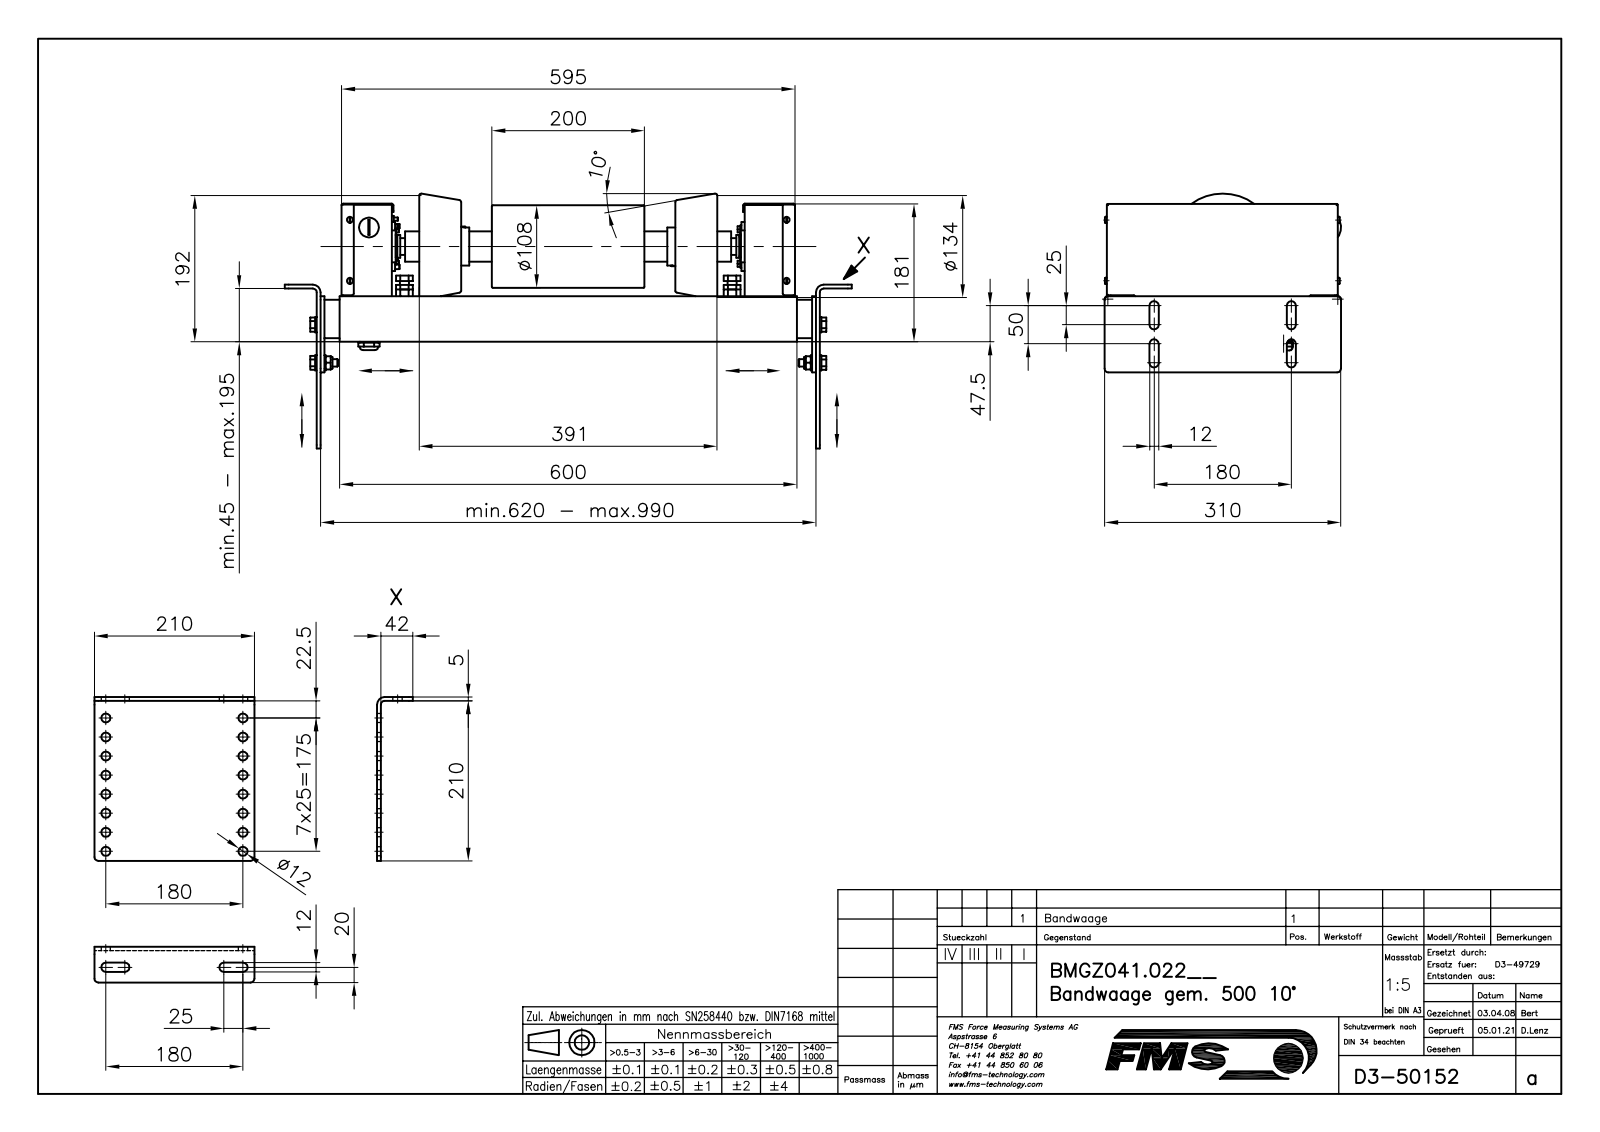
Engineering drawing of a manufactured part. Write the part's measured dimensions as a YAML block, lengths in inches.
part_name: "B50152_STP; B50028; 6KT-SCHRAUBE_M12X30; ZYL_SCHR__M4X8 (+8 more)"
step_written_by: "Mechanical Desktop 2009 (CONFIG_CONTROL_DESIGN)"
units: inches
bodies: {solids: 159, faces: 2640, planar: 1351, cylindrical: 946, other: 343}
overall_size: [29.291, 13.17, 12.213]
volume: 325.3
surface_area: 3782
round_holes:
  - {diameter: 0.472, count: 17}
  - {diameter: 0.197, count: 6}
  - {diameter: 0.138, count: 4}
  - {diameter: 0.193, count: 4}
  - {diameter: 0.252, count: 4}
  - {diameter: 0.342, count: 4}
  - {diameter: 0.344, count: 4}
  - {diameter: 0.394, count: 4}
  - {diameter: 0.413, count: 4}
  - {diameter: 0.42, count: 4}
  - {diameter: 0.583, count: 4}
  - {diameter: 0.161, count: 3}
round_bosses_or_shafts:
  - {diameter: 0.472, count: 11}
  - {diameter: 0.323, count: 8}
  - {diameter: 0.165, count: 8}
  - {diameter: 0.787, count: 6}
  - {diameter: 0.394, count: 6}
  - {diameter: 0.197, count: 5}
  - {diameter: 0.63, count: 4}
  - {diameter: 0.437, count: 4}
partial_cylinders:
  - {radius: 0.079, count: 34}
  - {radius: 0.039, count: 24}
  - {radius: 0.157, count: 16}
  - {radius: 0.197, count: 16}
  - {radius: 0.236, count: 14}
  - {radius: 0.138, count: 8}
  - {radius: 0.089, count: 6}
  - {radius: 0.02, count: 4}
face_to_face_distances: [0.157, 0.197, 0.039, 0.118, 1.083, 25.591, 1.417, 10.63, 2.598, 2.559]
hole_center_spacings: [0.984, 7.155, 1.969, 7.355, 2.953, 7.677, 3.937, 7.087]
